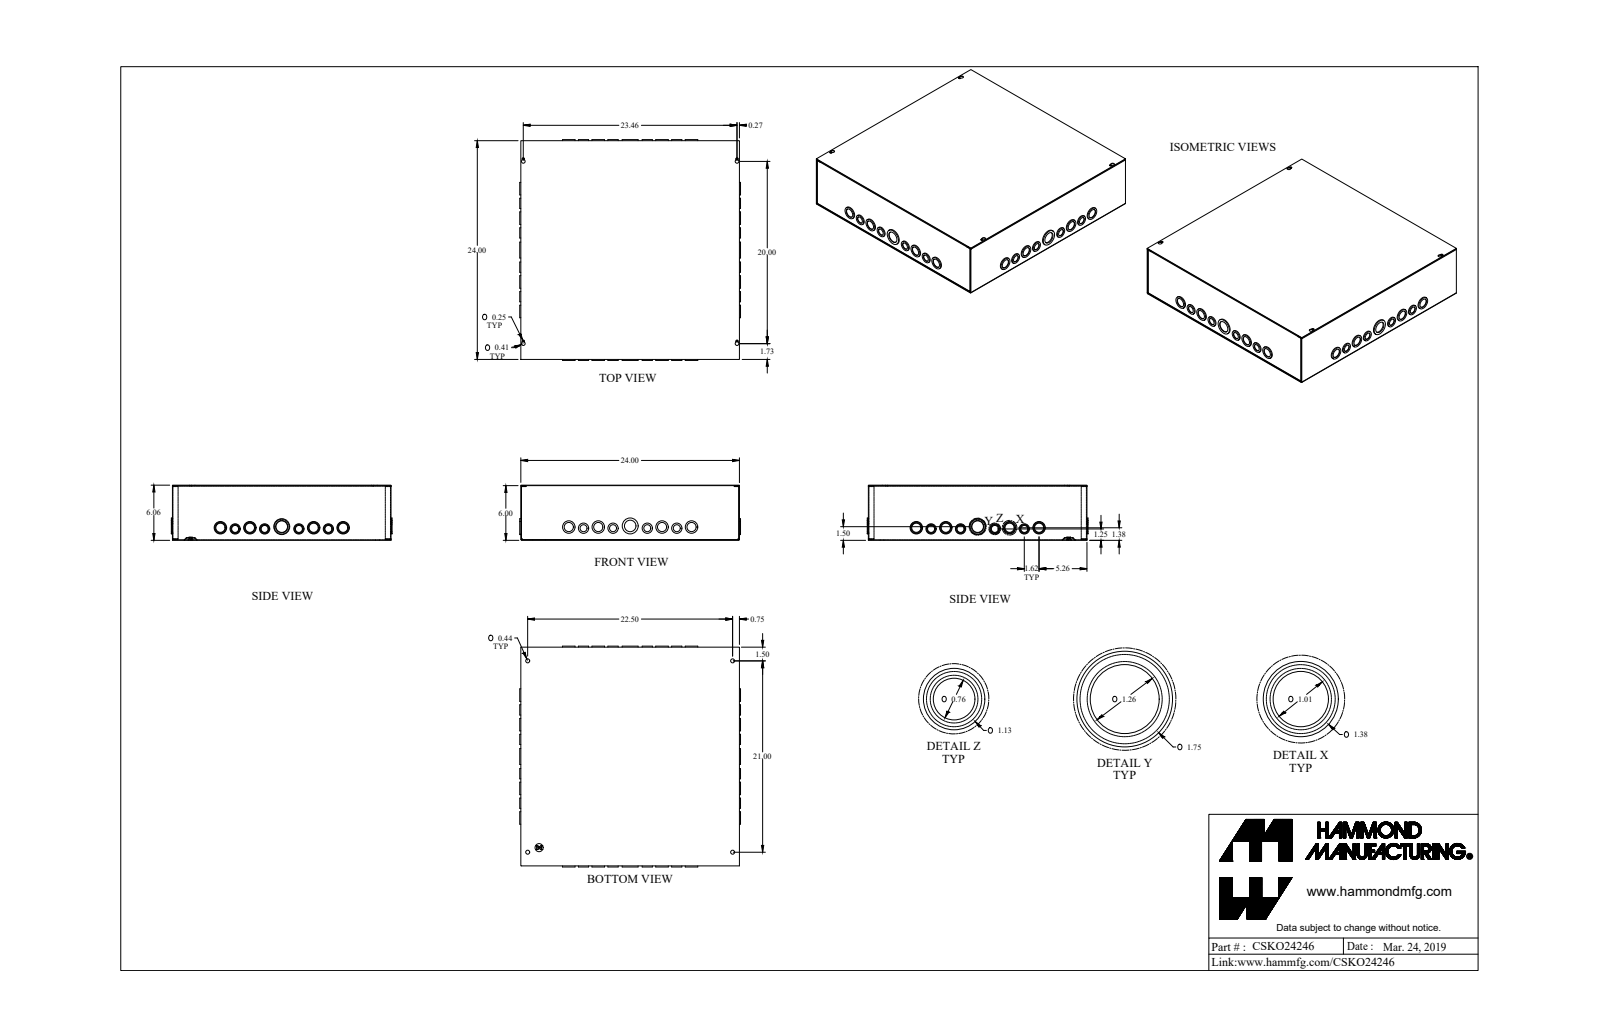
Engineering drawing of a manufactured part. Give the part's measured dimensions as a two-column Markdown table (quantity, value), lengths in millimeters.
| quantity | value |
| --- | --- |
| part name | CSKO24246_Default |
| STEP written by | SolidWorks 2019 (CONFIG_CONTROL_DESIGN) |
| units | millimeters |
| bodies | 4 solids, 637 faces (269 planar, 360 cylindrical, 8 other) |
| overall size | 615.5 × 615.5 × 153.8 |
| volume | 1 699 000 mm³ |
| surface area | 2 360 000 mm² |
| round holes (diameter × count) | 25.7 × 16, 32 × 10, 19.3 × 8, 4.3 × 5, 11.1 × 4, 41.6 × 2, 12.7 × 1 |
| round bosses / shafts (diameter × count) | 28.6 × 14, 34.9 × 9, 22.2 × 8, 22.2 × 6, 28.6 × 4, 34.9 × 3, 44.5 × 2, 12.5 × 1 |
| partial cylindrical surfaces (radius × count) | 0.7 × 12, 2.2 × 12, 1.4 × 8, 3.2 × 4, 5.2 × 4 |
| main face-to-face distances | 1.4, 152.4, 151, 153.8, 608.2, 609.6, 606.7, 2.9, 2, 148.9 |
| hole center spacings | 41.3, 82.3, 219, 177.8, 260.1, 17.6, 48.2, 89 |
